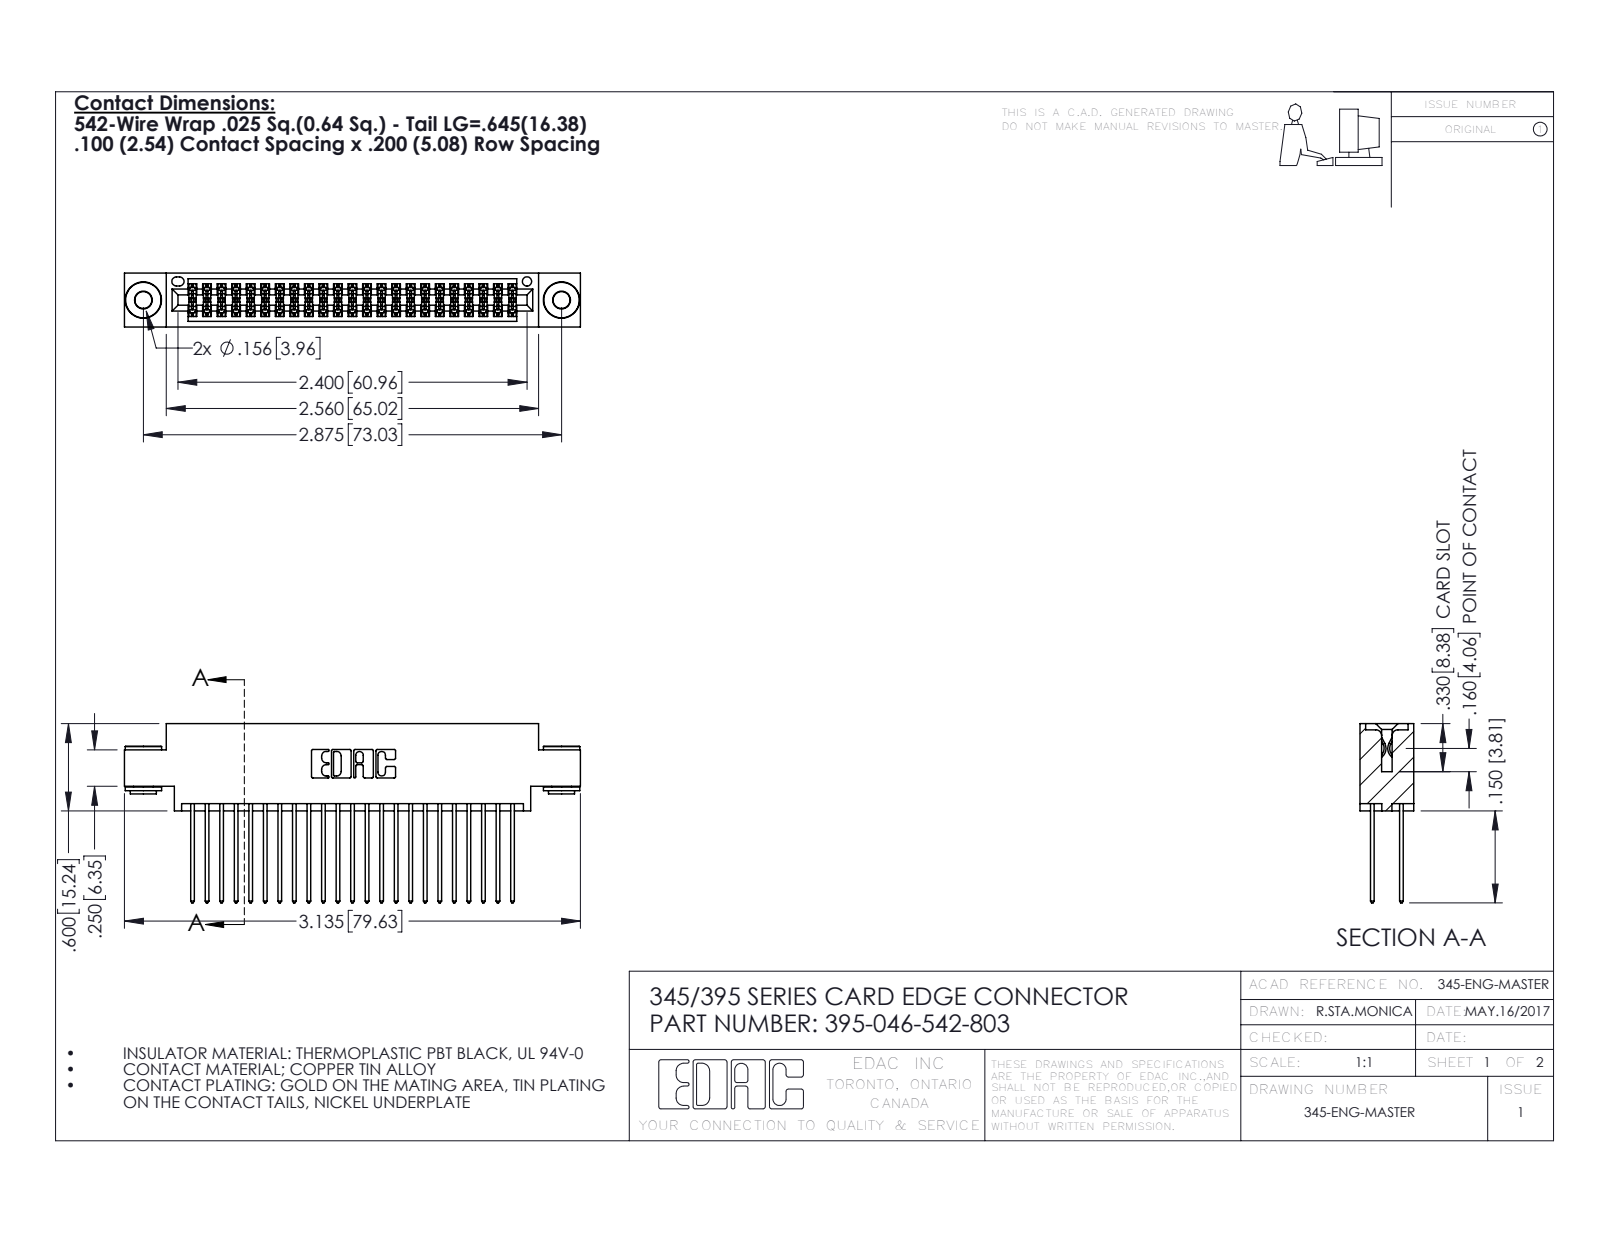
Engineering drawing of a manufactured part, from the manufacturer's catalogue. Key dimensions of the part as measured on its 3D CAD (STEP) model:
Part name (STEP PRODUCT): 345-292-001_345-293-142; 345-250-002_345-250-002-102; 345 Part_0.170 Offset - 0.156 Dia-TH; 395-046-542-803
STEP written by: SolidWorks 2016 (CONFIG_CONTROL_DESIGN)
Units: inches
Bodies: 49 solids, 2468 faces (1612 planar, 848 cylindrical, 8 other)
Overall size (bounding box): 3.135 × 1.232 × 0.37
Volume: 0.469 in³ · Surface area: 19.12 in²
Round holes (diameter × count): ⌀0.116 ×2, ⌀0.156 ×2, ⌀0.064 ×1
Round bosses / shafts (diameter × count): ⌀0.25 ×2, ⌀0.18 ×2, ⌀0.136 ×2
Partial cylindrical surfaces — rounded edges, fillets, slot ends (radius × count): R0.006 ×69, R0.01 ×46, R0.01 ×22, R0.007 ×6, R0.031 ×6, R0.026 ×3, R0.014 ×2, R0.019 ×2
Main face-to-face distances: 0.072, 0.298, 0.2, 0.098, 0.272, 0.025, 0.37, 0.225, 0.175, 0.1
Hole centre spacings: 0.27, 2.641, 2.875
